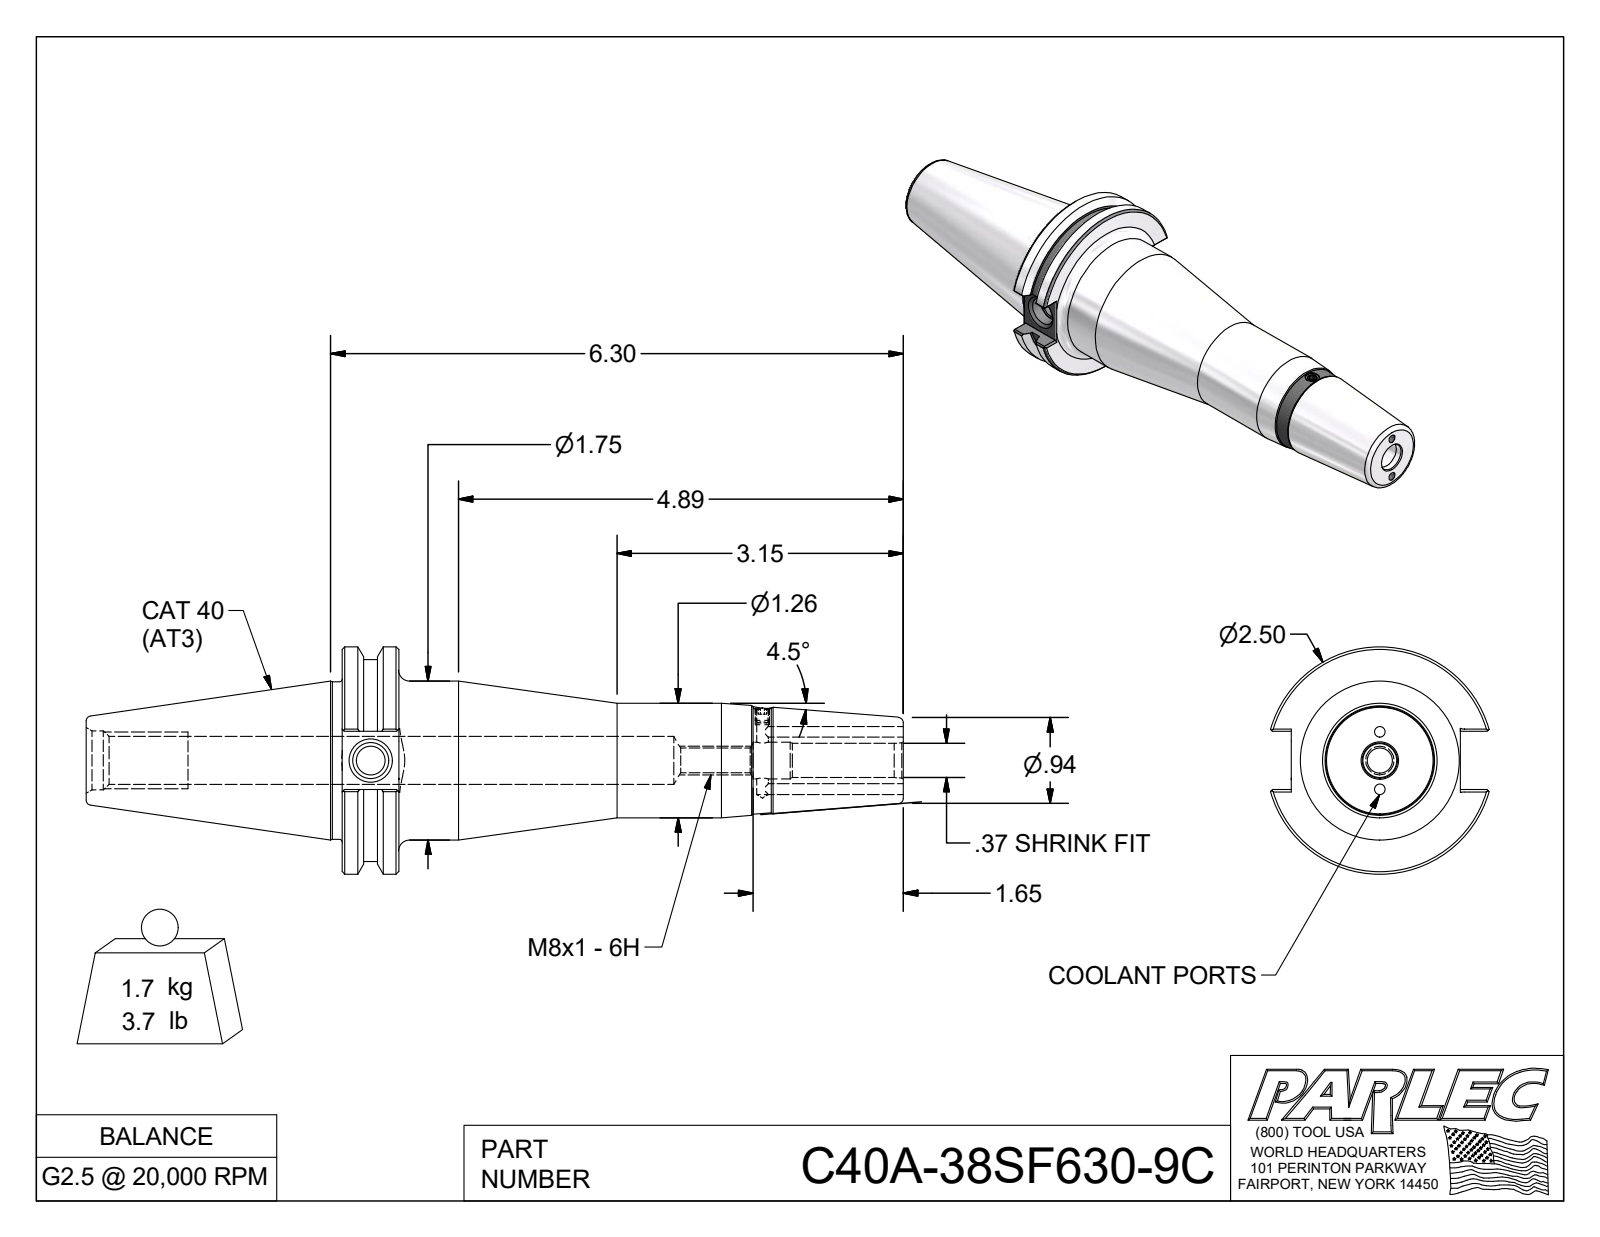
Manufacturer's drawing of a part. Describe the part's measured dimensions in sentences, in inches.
The part is named "C40A-38SF630-9C; 029-060". Its 3-D file was written by "Autodesk Inventor 2018 (AUTOMOTIVE_DESIGN)". It is 2 solids with 97 faces: 42 planar, 22 cylindrical and 33 other. Overall it measures 8.987 by 2.5 by 2.403 inches. Its volume is 13.25 cubic inches and its surface area 62.12 square inches. Round holes: 2 of diameter 0.118, 1 of diameter 0.128, 1 of diameter 0.197, 1 of diameter 0.272, 1 of diameter 0.315, 1 of diameter 0.374, 1 of diameter 0.396, 1 of diameter 0.404, 1 of diameter 0.527, 1 of diameter 0.648. Round bosses or shafts: 1 of diameter 2.5, 1 of diameter 2.219, 1 of diameter 1.75, 1 of diameter 1.73, 1 of diameter 1.26, 1 of diameter 0.157. The main face-to-face distances are 0.625, 6.174, 5.549, 0.64, 1.86, 2.812, 3.437, 8.987, 3.201, 0.389. The hole center spacings are 0.315, 0.63.
